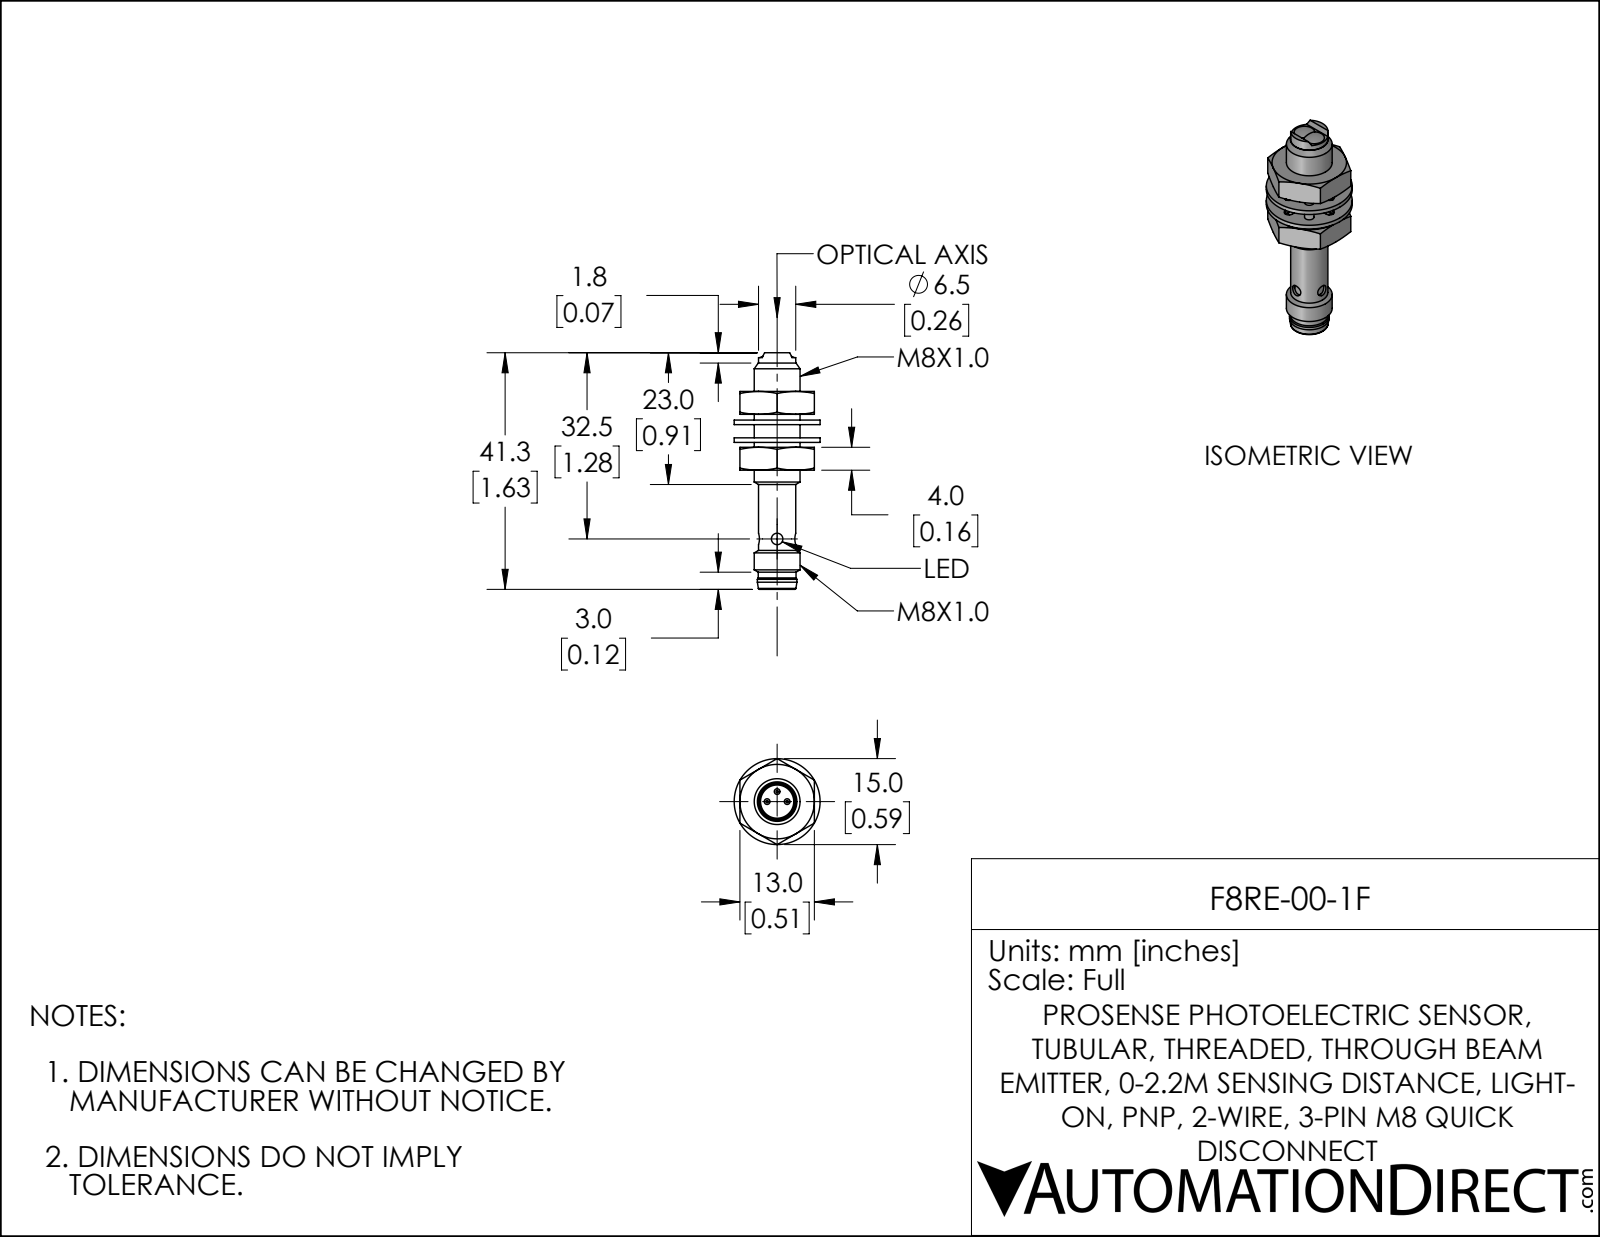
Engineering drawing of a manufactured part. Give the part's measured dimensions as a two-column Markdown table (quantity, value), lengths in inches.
| quantity | value |
| --- | --- |
| part name | F8RE-00-1F |
| STEP written by | SolidWorks 2019 (CONFIG_CONTROL_DESIGN) |
| units | inches |
| bodies | 5 solids, 157 faces (63 planar, 54 cylindrical, 40 other) |
| overall size | 1.626 × 0.591 × 0.591 |
| volume | 0.162 in³ |
| surface area | 4.169 in² |
| round holes (diameter × count) | 0.079 × 2, 0.228 × 1, 0.272 × 1 |
| round bosses / shafts (diameter × count) | 0.039 × 3, 0.591 × 1, 0.315 × 1, 0.272 × 1, 0.26 × 1, 0.256 × 1 |
| partial cylindrical surfaces (radius × count) | 0.032 × 8, 0.109 × 1, 0.165 × 1 |
| main face-to-face distances | 0.122, 0.031, 0.512, 0.384, 0.157, 0.154, 0.091, 0.033, 0.065, 0.197 |
